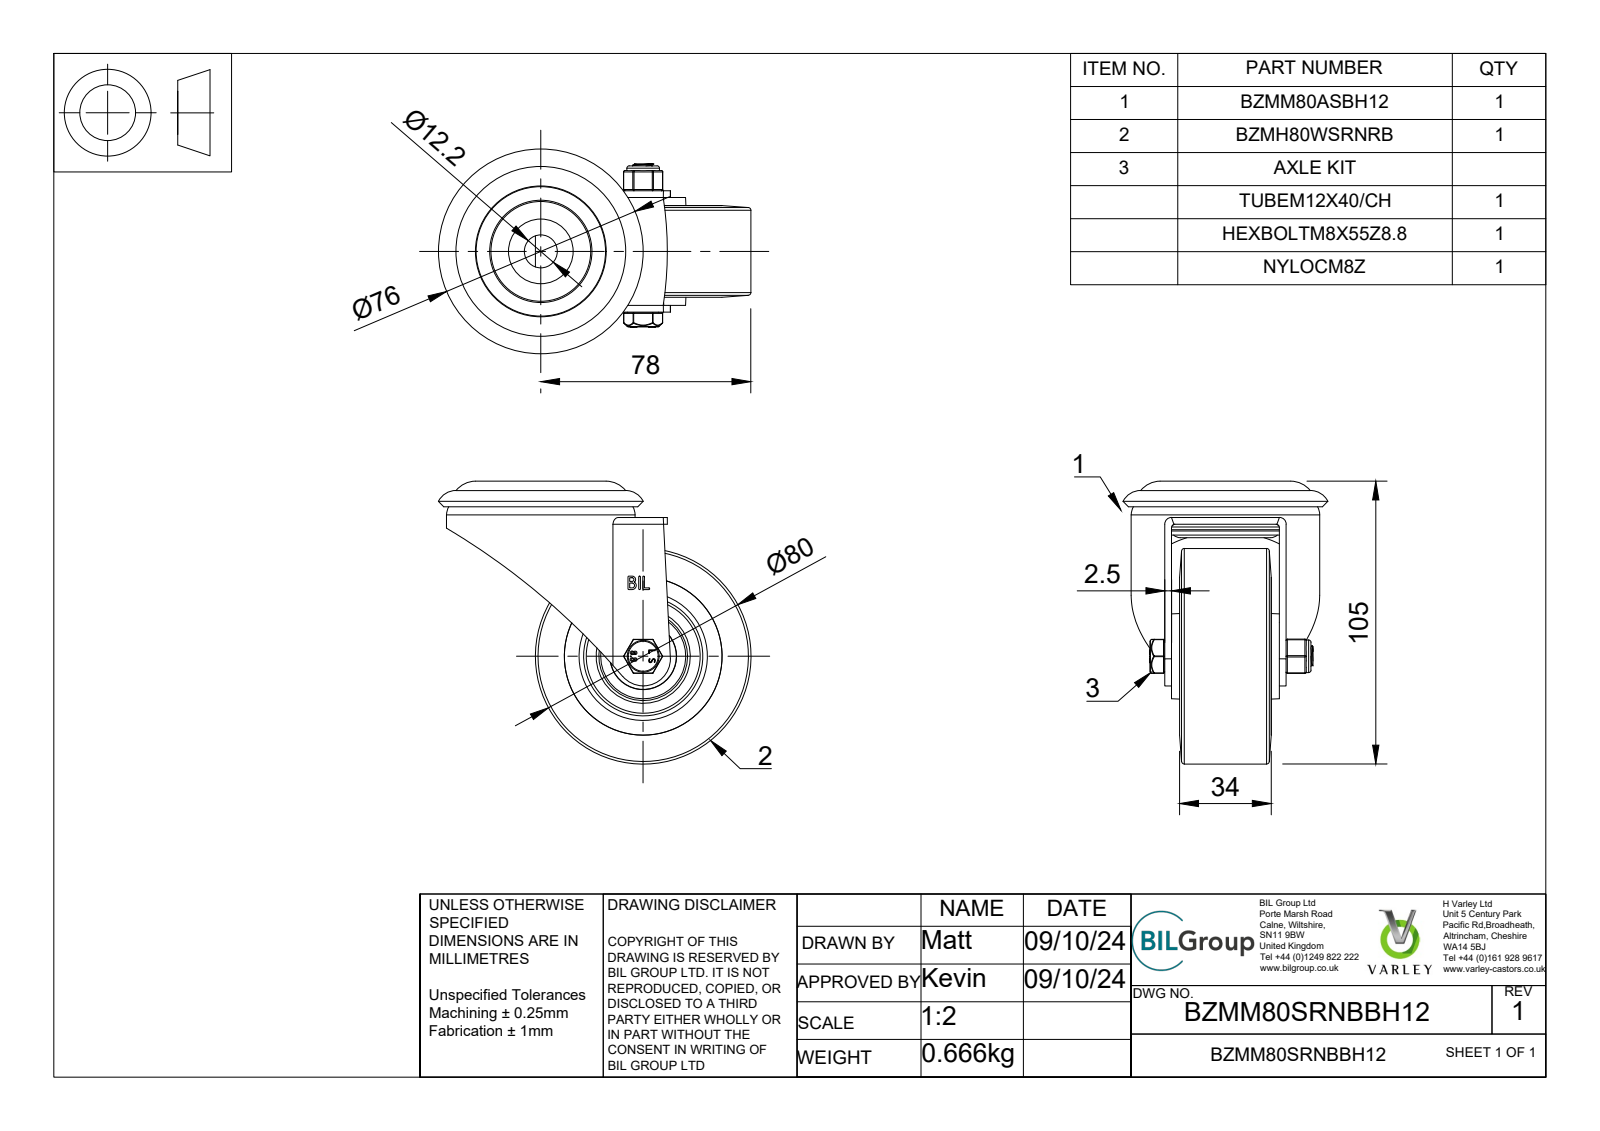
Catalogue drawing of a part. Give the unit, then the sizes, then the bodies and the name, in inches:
Units: inches
Overall size (bounding box): 4.567 × 4.134 × 2.992
Round holes (diameter × count): ⌀0.026 ×2, ⌀0.315 ×1, ⌀0.323 ×1, ⌀0.331 ×1, ⌀0.339 ×1, ⌀0.48 ×1, ⌀0.492 ×1, ⌀0.496 ×1, ⌀0.807 ×1, ⌀0.976 ×1, ⌀2.303 ×1, ⌀2.559 ×1
Round bosses / shafts (diameter × count): ⌀0.148 ×8, ⌀3.15 ×1, ⌀2.756 ×1, ⌀1.949 ×1, ⌀1.496 ×1, ⌀0.969 ×1, ⌀0.945 ×1, ⌀0.839 ×1
Partial cylindrical surfaces — rounded edges, fillets, slot ends (radius × count): R0.02 ×18, R0.01 ×12, R0.013 ×4, R0.025 ×4, R0.049 ×4, R0.025 ×2, R0.025 ×2, R0.098 ×2
Main face-to-face distances: 0.098, 0.118, 1.673, 0.217, 1.555, 1.457, 1.575, 0.177, 0.039, 0.079
Hole centre spacings: 0.127, 0.098
Volume: 12.2 in³ · Surface area: 144.3 in²
Bodies: 18 solids, 442 faces (179 planar, 157 cylindrical, 106 other)
Part name (STEP PRODUCT): BZMM80SRNBBH12 v3; BZMM80ASBH12 v1; ZINC PLATED, PRESSED STEEL FORKS; ZINC PLATED, PRESSED STEEL TOP PLATE (+7 more)
STEP written by: Autodesk Translation Framework v13.20.0.188 (AUTOMOTIVE_DESIGN)
